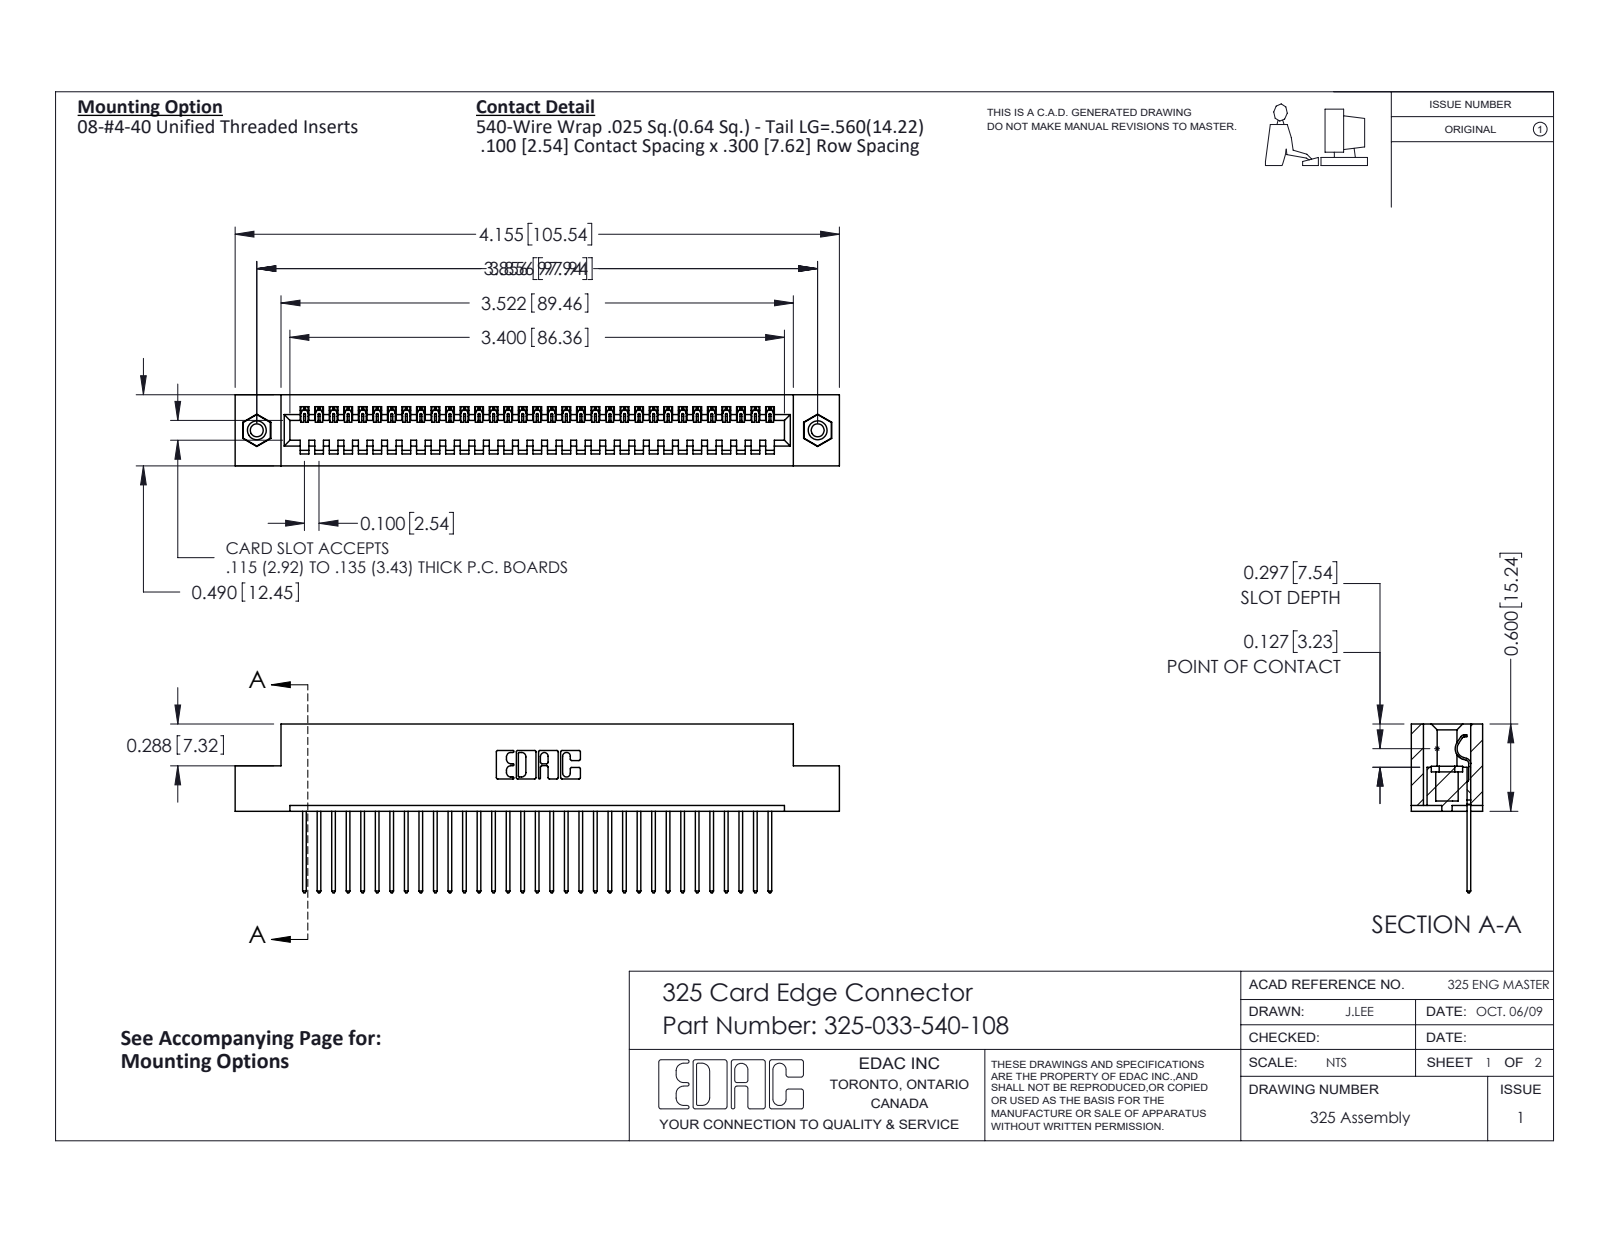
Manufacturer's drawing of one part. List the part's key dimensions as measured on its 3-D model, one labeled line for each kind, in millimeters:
Part name (STEP PRODUCT): 325 Part_TI; 325-292-001_325-293-140; 325-033-540-108; 345-250-001_345-250-003-102
STEP written by: SolidWorks 2016 (CONFIG_CONTROL_DESIGN)
Units: millimetres
Bodies: 36 solids, 2088 faces (1488 planar, 584 cylindrical, 16 other)
Overall size (bounding box): 105.5 × 29.5 × 12.4
Volume: 13 400 mm³ · Surface area: 14 790 mm²
Round holes (diameter × count): ⌀2.3 ×2, ⌀3.2 ×2, ⌀4.1 ×2
Round bosses / shafts (diameter × count): ⌀3.9 ×2
Partial cylindrical surfaces — rounded edges, fillets, slot ends (radius × count): R0.2 ×66, R0.3 ×66, R0.3 ×22, R0.2 ×6, R0.8 ×6, R0.7 ×3, R0.4 ×1, R0.6 ×1
Main face-to-face distances: 2.1, 10.3, 12.4, 7.6, 2.7, 9.7, 0.6, 8.3, 14.2, 1
Hole centre spacings: 97.9
